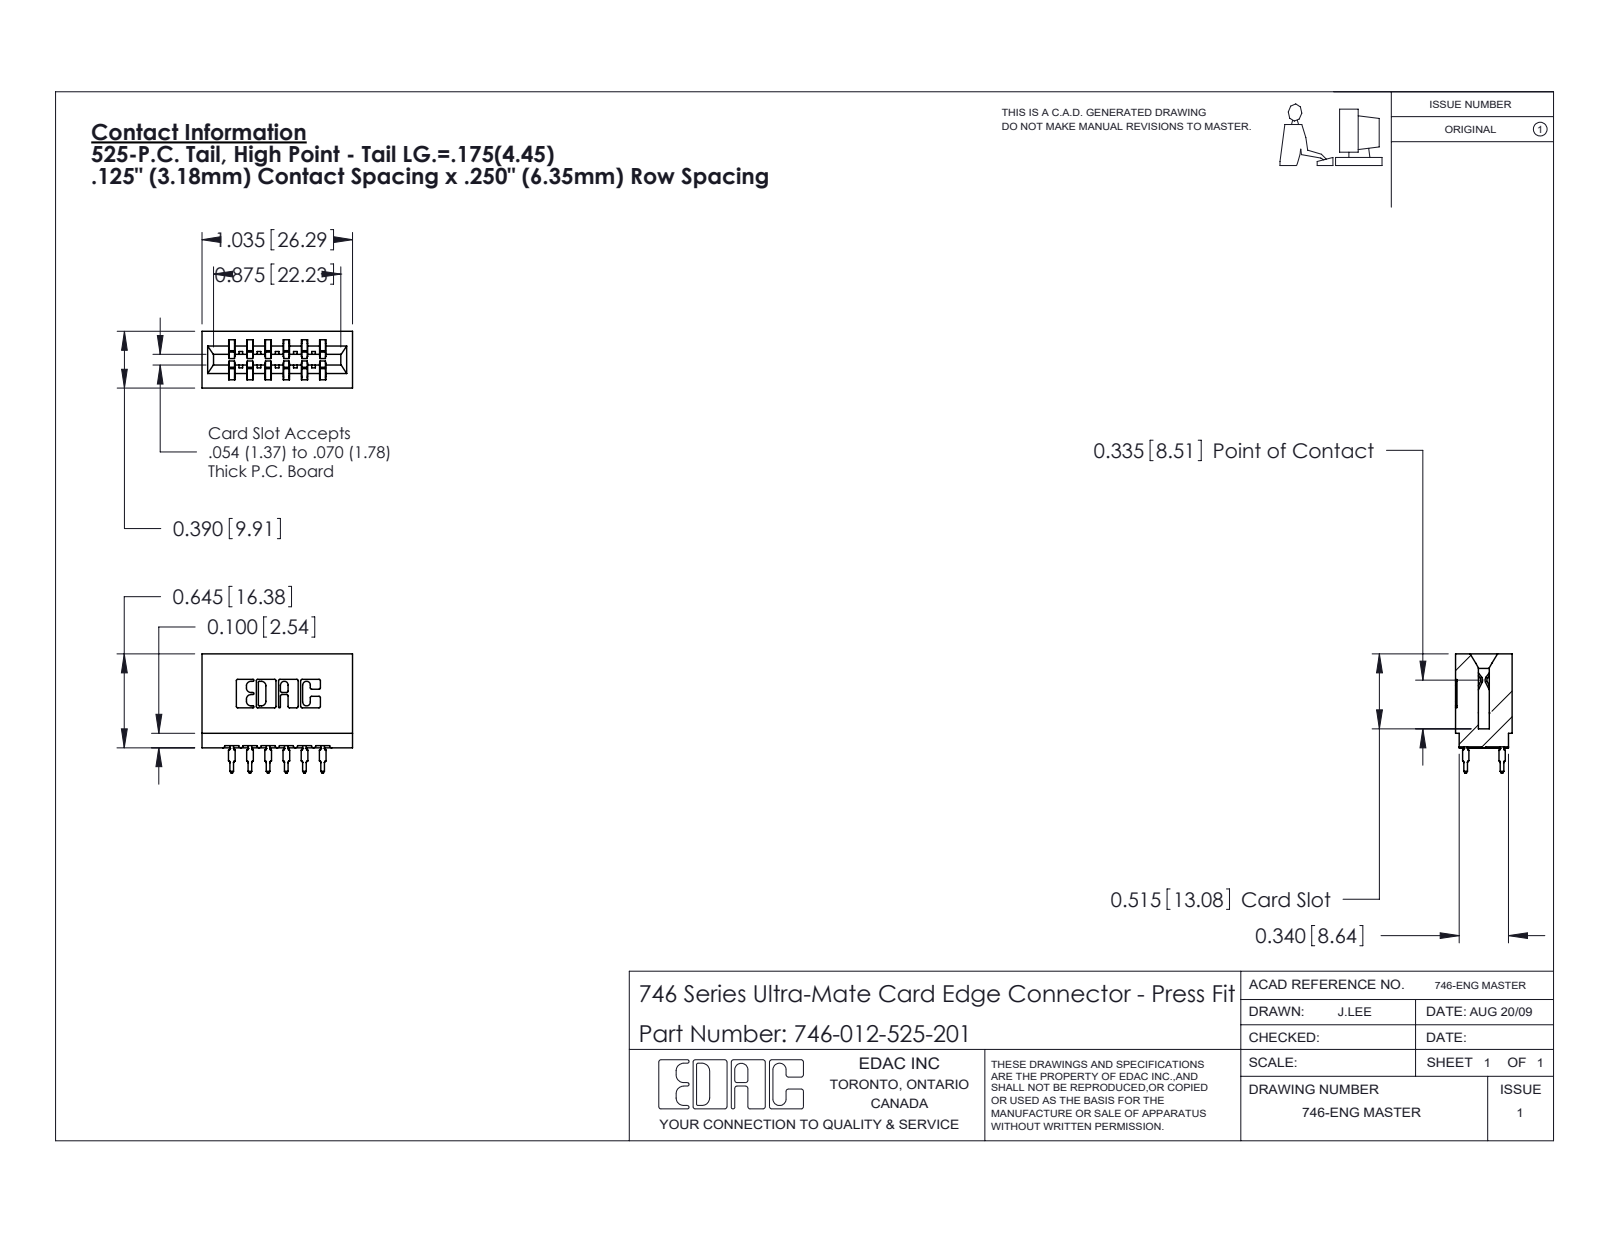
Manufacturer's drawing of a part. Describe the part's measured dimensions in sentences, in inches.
The part is named "746-292-001_525; 746-012-525-201; 746 Part_.515 Slot Depth - 01". Its 3-D file was written by "SolidWorks 2020 (CONFIG_CONTROL_DESIGN)". It is 13 solids with 1171 faces: 607 planar, 252 cylindrical and 312 other. Overall it measures 1.035 by 0.819 by 0.39 inches. Its volume is 0.186 cubic inches and its surface area 6.409 square inches. Partial cylindrical surfaces (rounded edges, fillets, slot ends): 24 of radius 0.021, 22 of radius 0.01, 8 of radius 0.005, 8 of radius 0.011, 7 of radius 0.015, 6 of radius 0.007, 6 of radius 0.031, 3 of radius 0.026. The main face-to-face distances are 0.25, 0.125, 0.042, 0.057, 0.333, 0.125, 0.39, 0.292, 0.208, 0.375.
